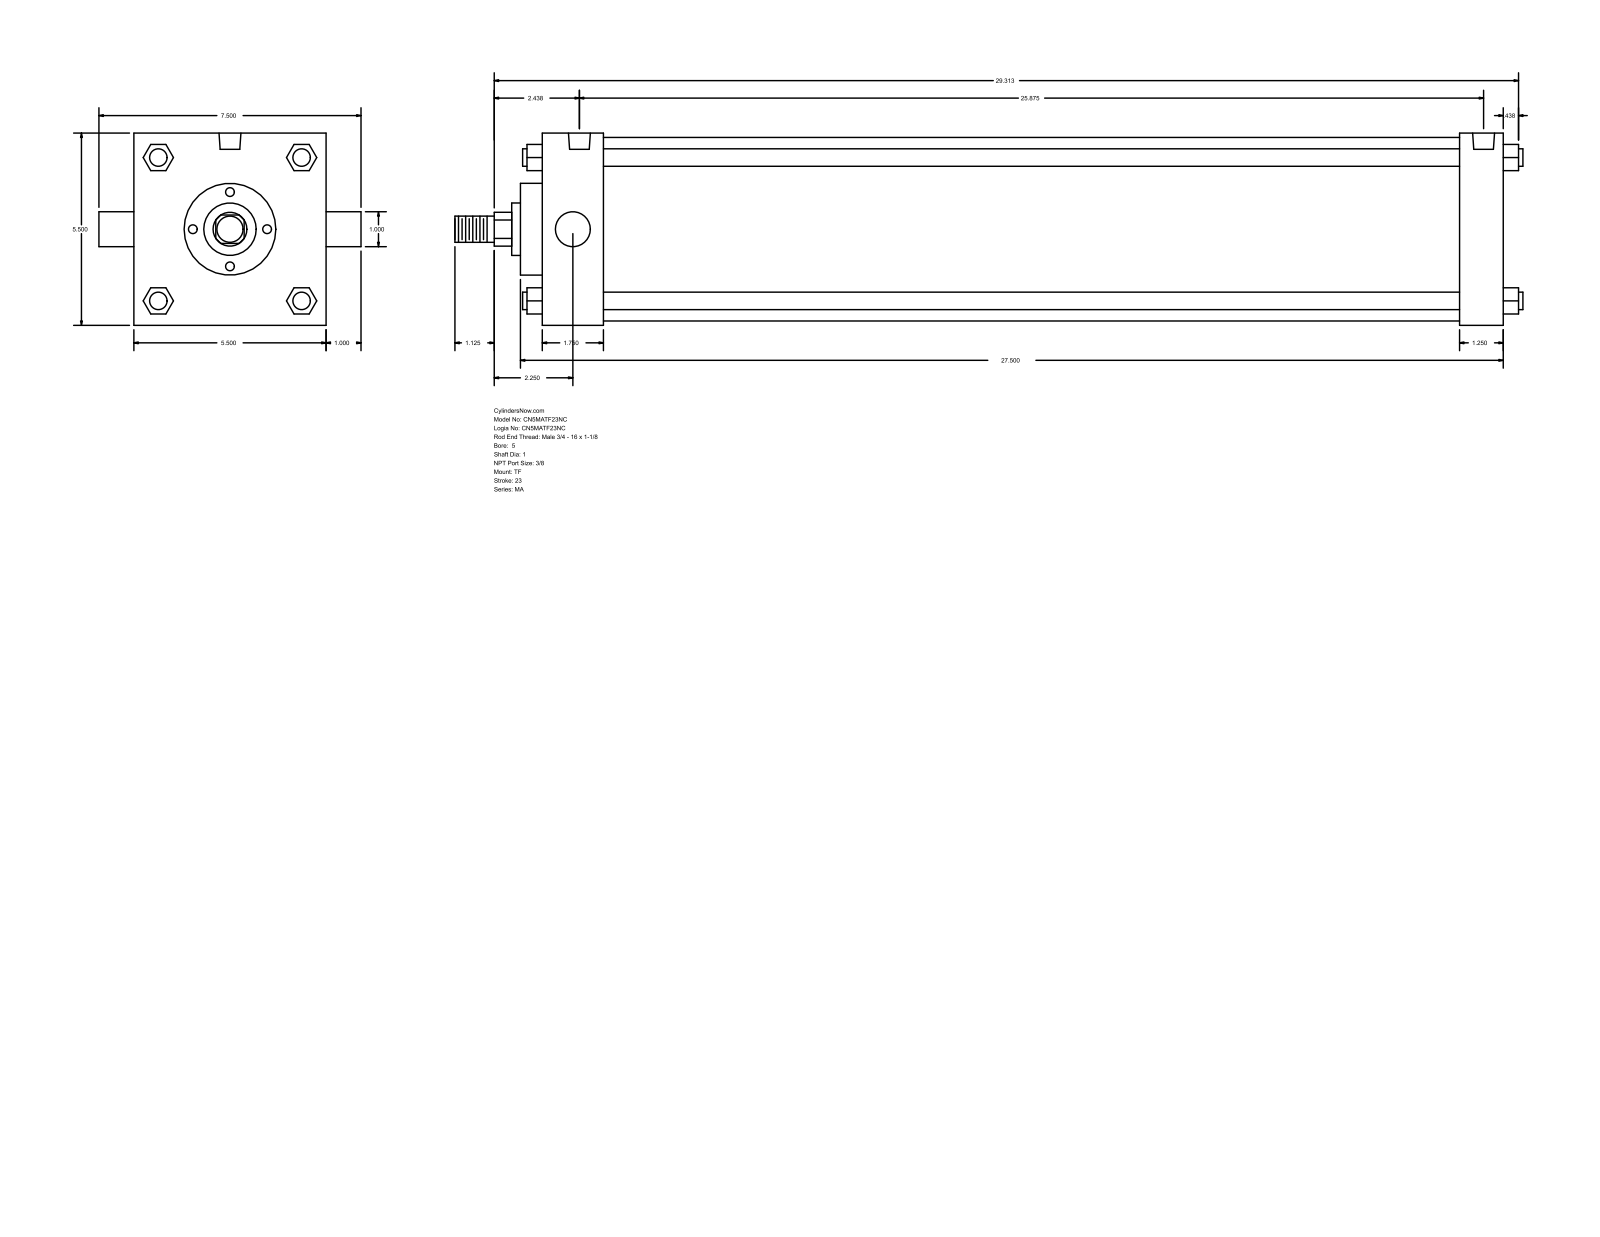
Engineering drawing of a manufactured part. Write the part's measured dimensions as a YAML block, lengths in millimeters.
part_name: "MA_TF__0500_1"
step_written_by: "GSSL Pune (CONFIG_CONTROL_DESIGN)"
units: millimeters
bodies: {solids: 0, faces: 122, planar: 93, cylindrical: 29, other: 0}
overall_size: [776.29, 190.5, 139.7]
round_holes:
  - {diameter: 11.11, count: 3}
  - {diameter: 15.93, count: 2}
round_bosses_or_shafts:
  - {diameter: 12.7, count: 4}
  - {diameter: 25.4, count: 2}
  - {diameter: 133.35, count: 1}
  - {diameter: 66.67, count: 1}
  - {diameter: 38.1, count: 1}
  - {diameter: 19.05, count: 1}
partial_cylinders:
  - {radius: 12.29, count: 1}
face_to_face_distances: [139.7, 698.5, 666.75, 31.75, 44.46, 622.29, 654.04, 15.87, 60.33, 682.62]
hole_center_spacings: [4.76, 652.47, 647.71, 657.23]
